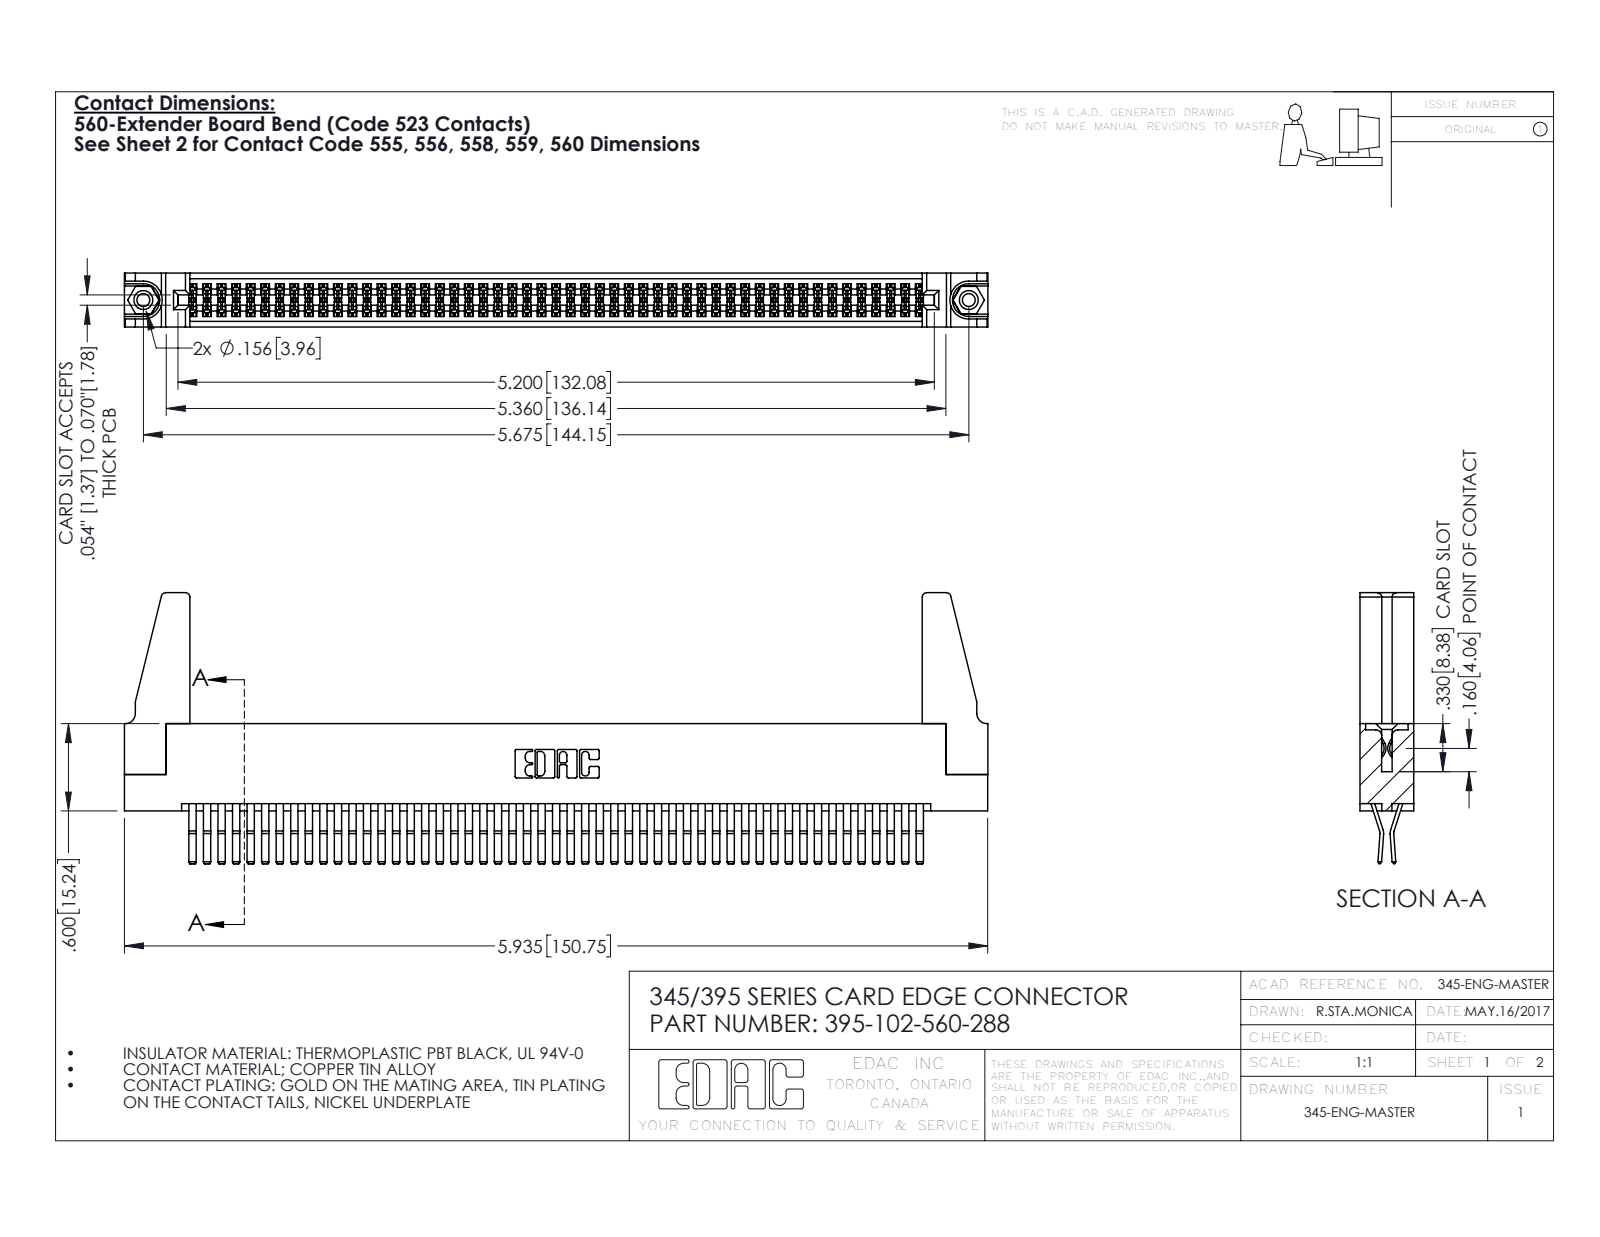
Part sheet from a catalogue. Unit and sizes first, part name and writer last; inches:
Units: inches
Overall size (bounding box): 5.936 × 1.862 × 0.37
Round holes (diameter × count): ⌀0.089 ×2, ⌀0.125 ×2, ⌀0.156 ×2, ⌀0.064 ×1
Round bosses / shafts (diameter × count): ⌀0.155 ×2
Partial cylindrical surfaces — rounded edges, fillets, slot ends (radius × count): R0.006 ×154, R0.01 ×22, R0.03 ×8, R0.007 ×6, R0.031 ×6, R0.026 ×3, R0.01 ×2, R0.014 ×2
Main face-to-face distances: 0.072, 0.298, 0.025, 0.37, 0.2, 0.098, 0.272, 0.225, 0.175, 0.149
Hole centre spacings: 0.27, 5.439, 5.675
Volume: 1.138 in³ · Surface area: 43.06 in²
Bodies: 107 solids, 5554 faces (3518 planar, 2020 cylindrical, 16 other)
Part name (STEP PRODUCT): 345 Part_Flush Mounting Lugs - 0.156 Dia-TH; 395-102-560-288; 345-220-078_345-220-088; 345-292-001_560 Tail (+1 more)
STEP written by: SolidWorks 2016 (CONFIG_CONTROL_DESIGN)
